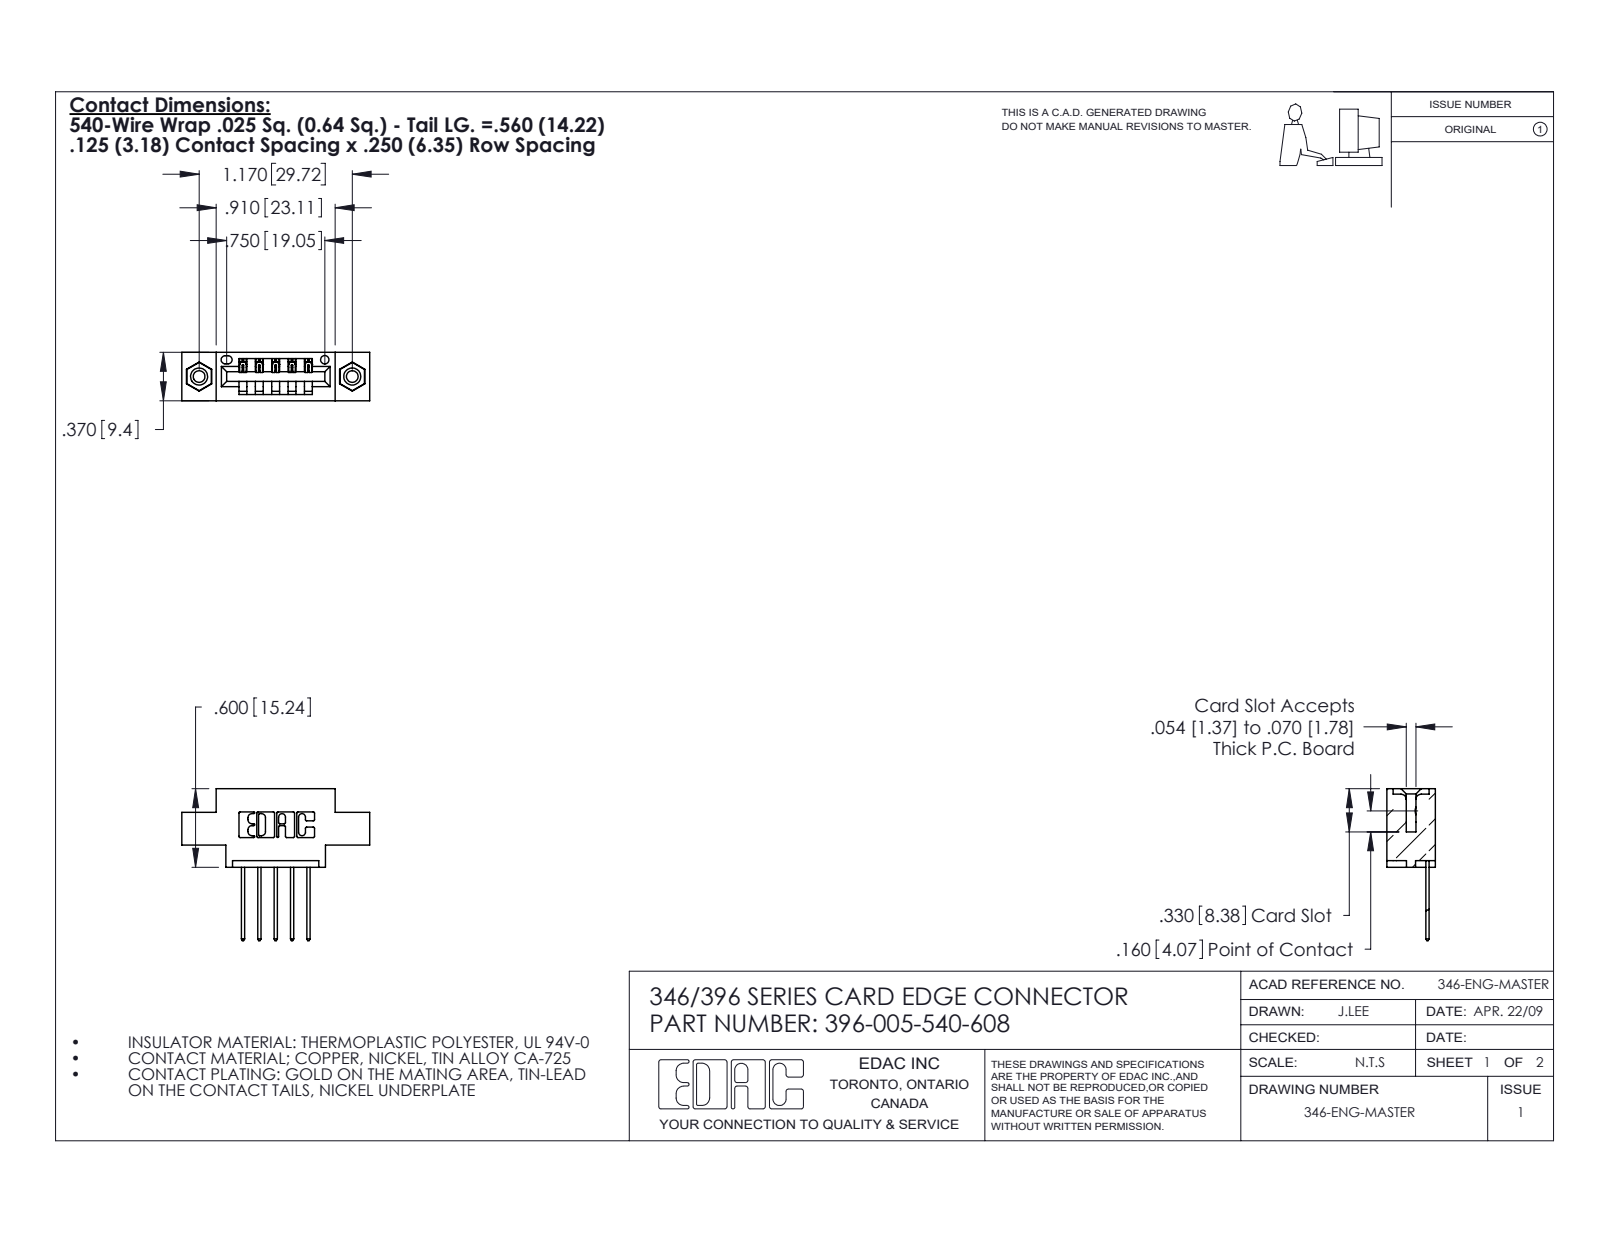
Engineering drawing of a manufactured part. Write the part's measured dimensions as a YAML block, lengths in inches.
part_name: "345-292-001_345-293-140; 346 Part_0.170 Offset - 0.156 Dia-TI; 345-250-001_345-250-003-102; 396-005-540-608"
step_written_by: "SolidWorks 2020 (CONFIG_CONTROL_DESIGN)"
units: inches
bodies: {solids: 8, faces: 476, planar: 312, cylindrical: 148, other: 16}
overall_size: [1.435, 1.16, 0.37]
volume: 0.188
surface_area: 5.706
round_holes:
  - {diameter: 0.089, count: 2}
  - {diameter: 0.125, count: 2}
  - {diameter: 0.156, count: 2}
  - {diameter: 0.064, count: 1}
round_bosses_or_shafts:
  - {diameter: 0.155, count: 2}
partial_cylinders:
  - {radius: 0.01, count: 22}
  - {radius: 0.006, count: 10}
  - {radius: 0.01, count: 10}
  - {radius: 0.007, count: 6}
  - {radius: 0.031, count: 6}
  - {radius: 0.026, count: 3}
  - {radius: 0.031, count: 2}
  - {radius: 0.04, count: 2}
face_to_face_distances: [0.25, 0.37, 0.048, 0.322, 0.222, 0.148, 0.072, 0.298, 0.025, 0.1]
hole_center_spacings: [0.246, 0.969, 1.17]
